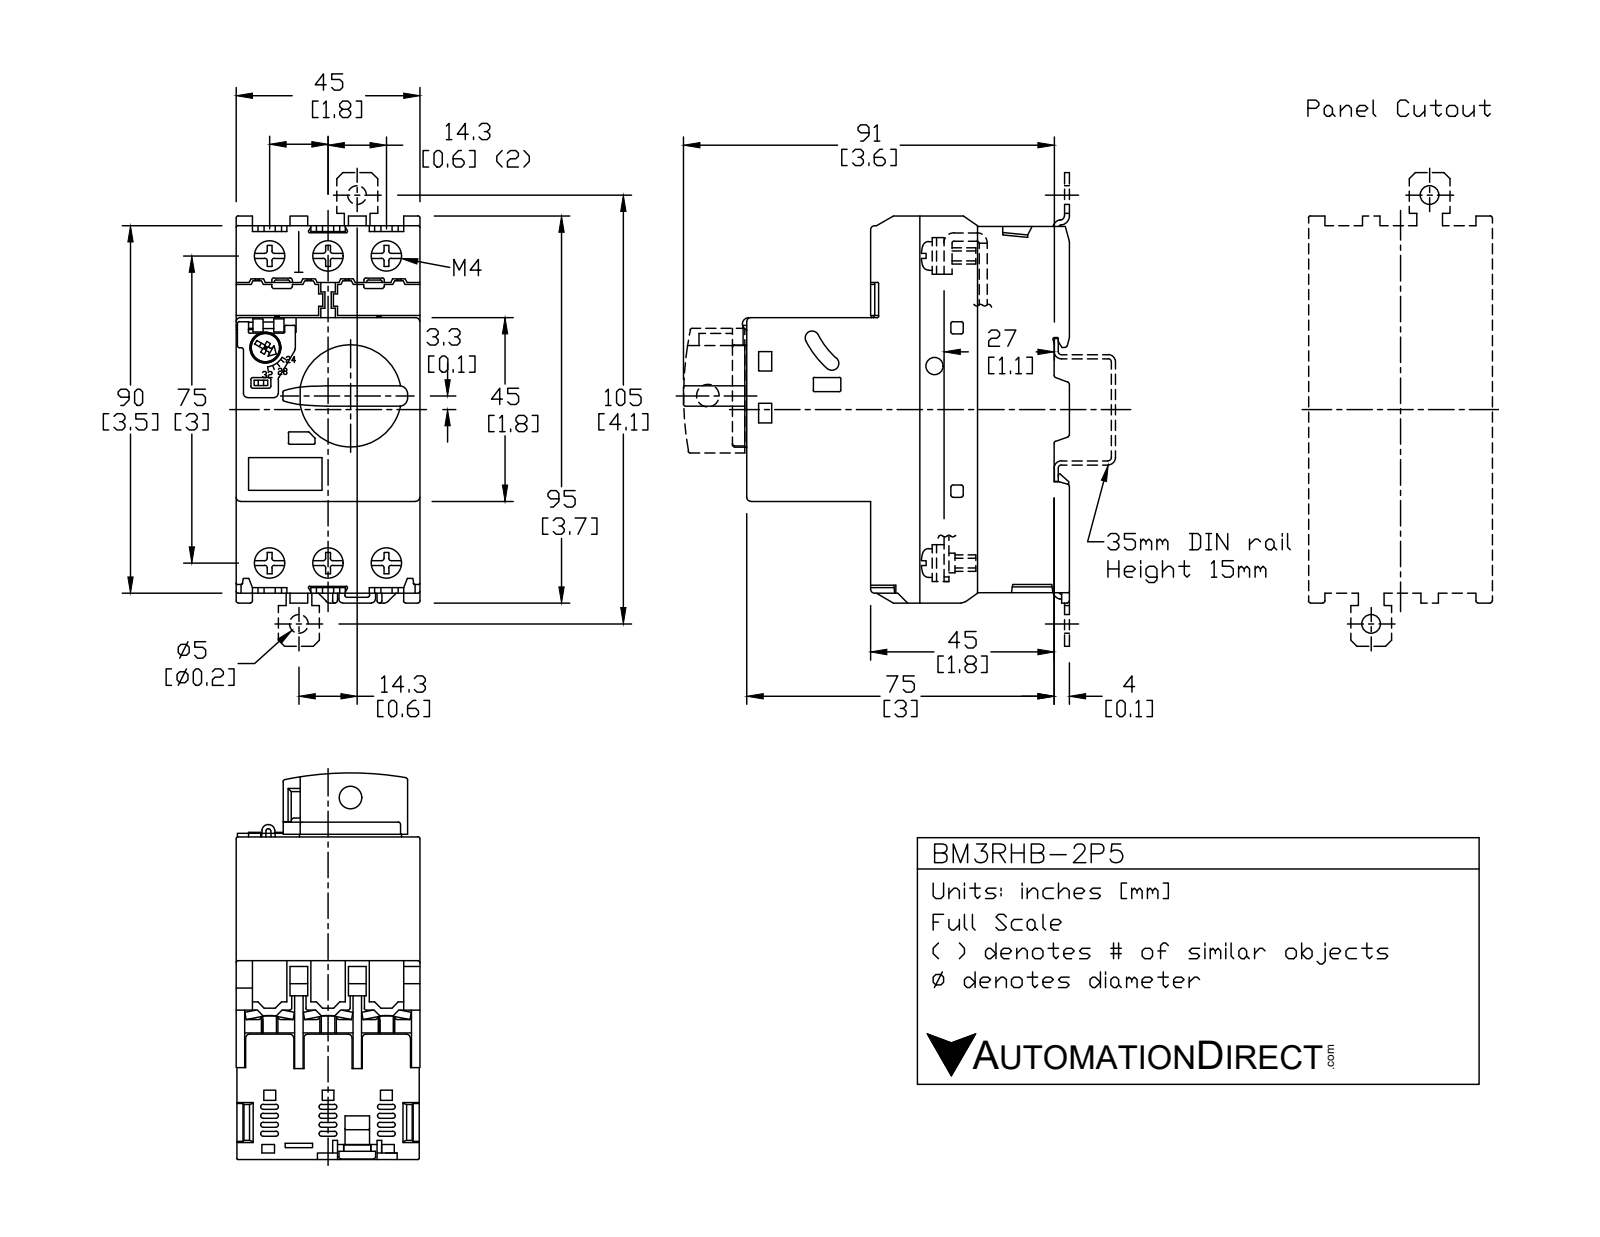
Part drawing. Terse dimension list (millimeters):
name: BM3RHB-2P5
written by: SolidWorks 2018 (AUTOMOTIVE_DESIGN)
unit: mm
bodies: 25 solids, 1294 faces (964 planar, 327 cylindrical, 3 other)
size: 94.8 × 94.5 × 45
volume: 231 500 mm³; area: 57 040 mm²
holes: 6× ⌀4, 6× ⌀7.4, 1× ⌀1.6, 1× ⌀4.2, 1× ⌀5, 1× ⌀5.5, 1× ⌀7.5
bosses: 6× ⌀6, 1× ⌀25, 1× ⌀7
rounds: 67× R0.5, 24× R0.6, 14× R2, 12× R0.3, 8× R1, 8× R2.5, 6× R0.2, 2× R1.5
face distances: 45, 36.6, 42.4, 79, 22.4, 67.4, 3, 16.5, 20.1, 12
hole spacings: 14.3, 76.4, 75, 28.6, 80.3, 22.4, 23.9, 27.1
